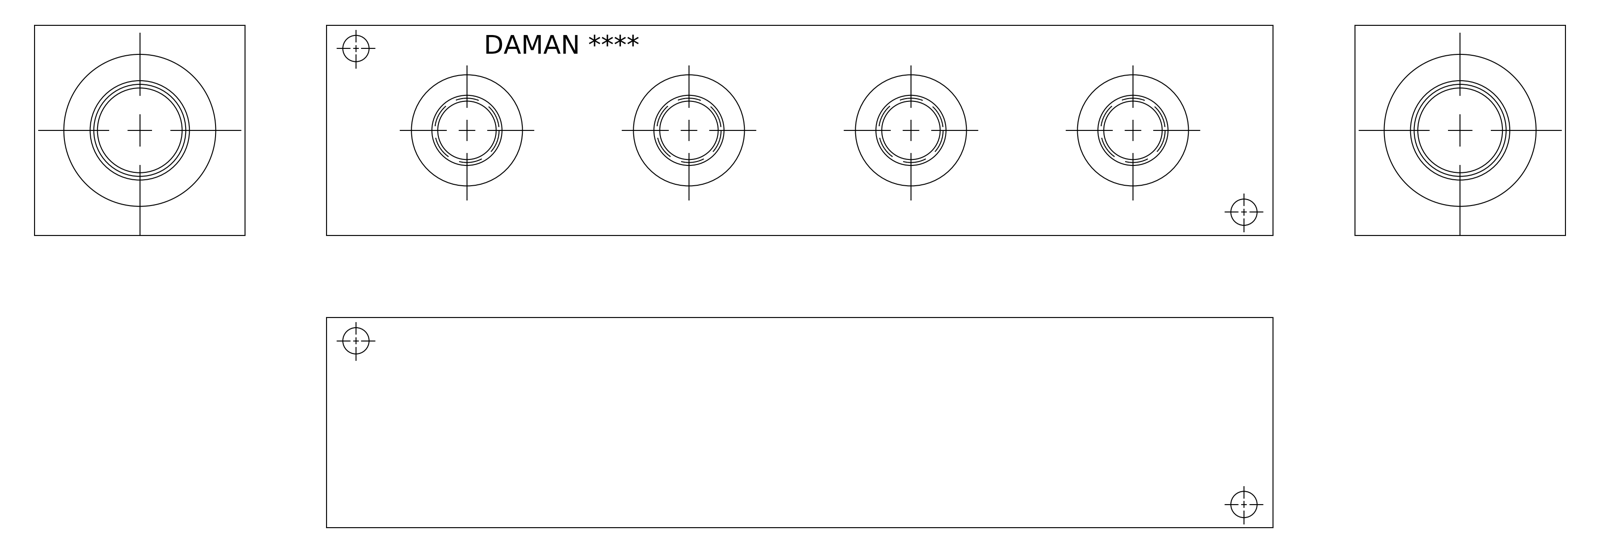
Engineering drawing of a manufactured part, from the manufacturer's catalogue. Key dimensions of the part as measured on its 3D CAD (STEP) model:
Part name (STEP PRODUCT): Part_SH0000408S_3D
STEP written by: Autodesk Inventor 2019 (AUTOMOTIVE_DESIGN)
Units: millimetres
Bodies: 1 solid, 382 faces (221 planar, 36 cylindrical, 125 other)
Overall size (bounding box): 257.18 × 57.15 × 57.15
Volume: 770 072 mm³ · Surface area: 79 936 mm²
Round holes (diameter × count): ⌀7.14 ×4, ⌀17.5 ×4, ⌀19.05 ×4, ⌀19.25 ×4, ⌀30.63 ×4, ⌀15.88 ×2, ⌀23.01 ×1, ⌀24.92 ×1, ⌀26.99 ×1, ⌀27.43 ×1, ⌀42.04 ×1
Main face-to-face distances: 57.15, 0.79, 257.18, 56.36, 256.39, 255.6, 42.09, 14.27, 15.06, 19.84
Hole centre spacings: 60.32, 120.65, 245.36, 37.45, 37.48, 60.33, 93.16, 93.19
